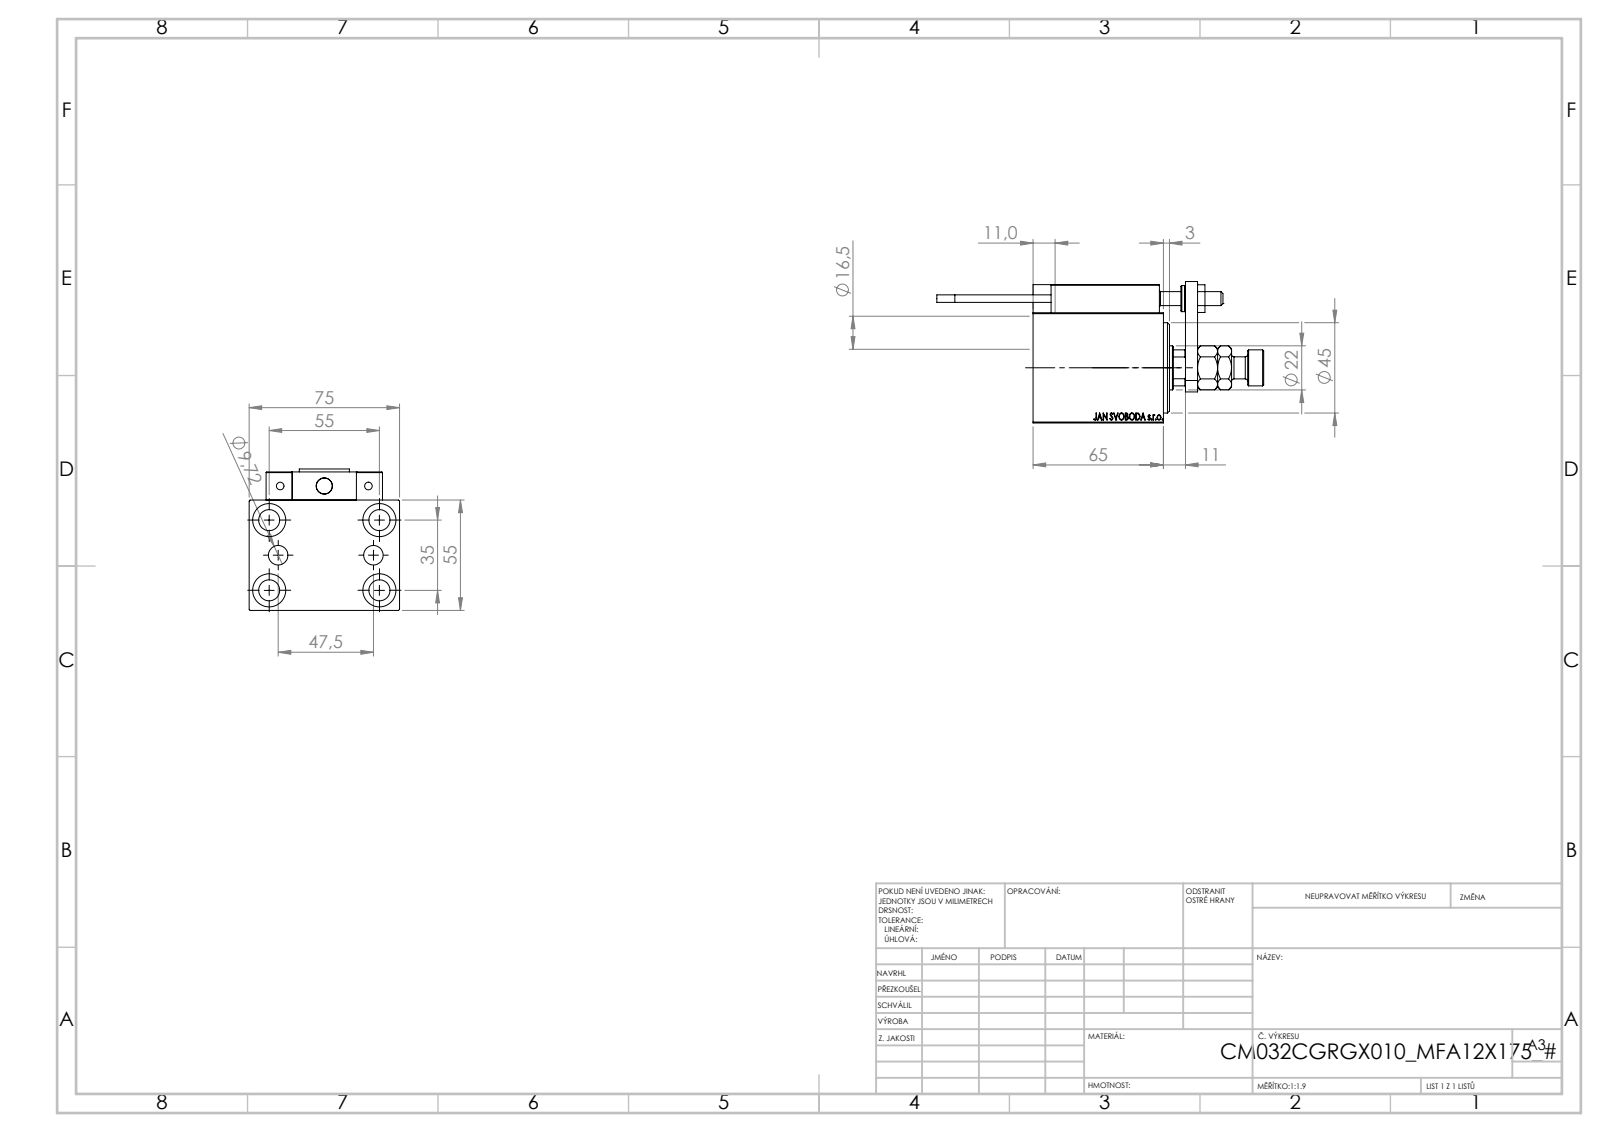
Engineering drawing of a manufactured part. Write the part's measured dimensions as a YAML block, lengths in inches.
part_name: "V450CM_VC_B; Block; NUT_D12; ALLEN BOLT D8 (+8 more)"
step_written_by: "SolidWorks 2019 (CONFIG_CONTROL_DESIGN)"
units: inches
bodies: {solids: 24, faces: 1330, planar: 576, cylindrical: 188, other: 566}
overall_size: [6.457, 2.953, 2.776]
volume: 17.59
surface_area: 119.9
round_holes:
  - {diameter: 0.157, count: 6}
  - {diameter: 0.315, count: 5}
  - {diameter: 0.413, count: 5}
  - {diameter: 0.65, count: 5}
  - {diameter: 0.126, count: 4}
  - {diameter: 0.197, count: 2}
  - {diameter: 0.383, count: 2}
  - {diameter: 0.276, count: 1}
  - {diameter: 0.866, count: 1}
  - {diameter: 1.004, count: 1}
  - {diameter: 1.26, count: 1}
  - {diameter: 1.339, count: 1}
round_bosses_or_shafts:
  - {diameter: 0.433, count: 2}
  - {diameter: 0.197, count: 2}
  - {diameter: 0.15, count: 2}
  - {diameter: 0.709, count: 1}
  - {diameter: 0.512, count: 1}
partial_cylinders:
  - {radius: 0.012, count: 30}
  - {radius: 0.118, count: 2}
  - {radius: 0.413, count: 1}
face_to_face_distances: [2.165, 2.953, 0.551, 0.906, 0.197, 1.772, 0.709, 0.394, 0.118, 2.717]
hole_center_spacings: [0.705, 1.283, 2.132, 0.448, 0.674, 0.787, 0.935, 1.094]
